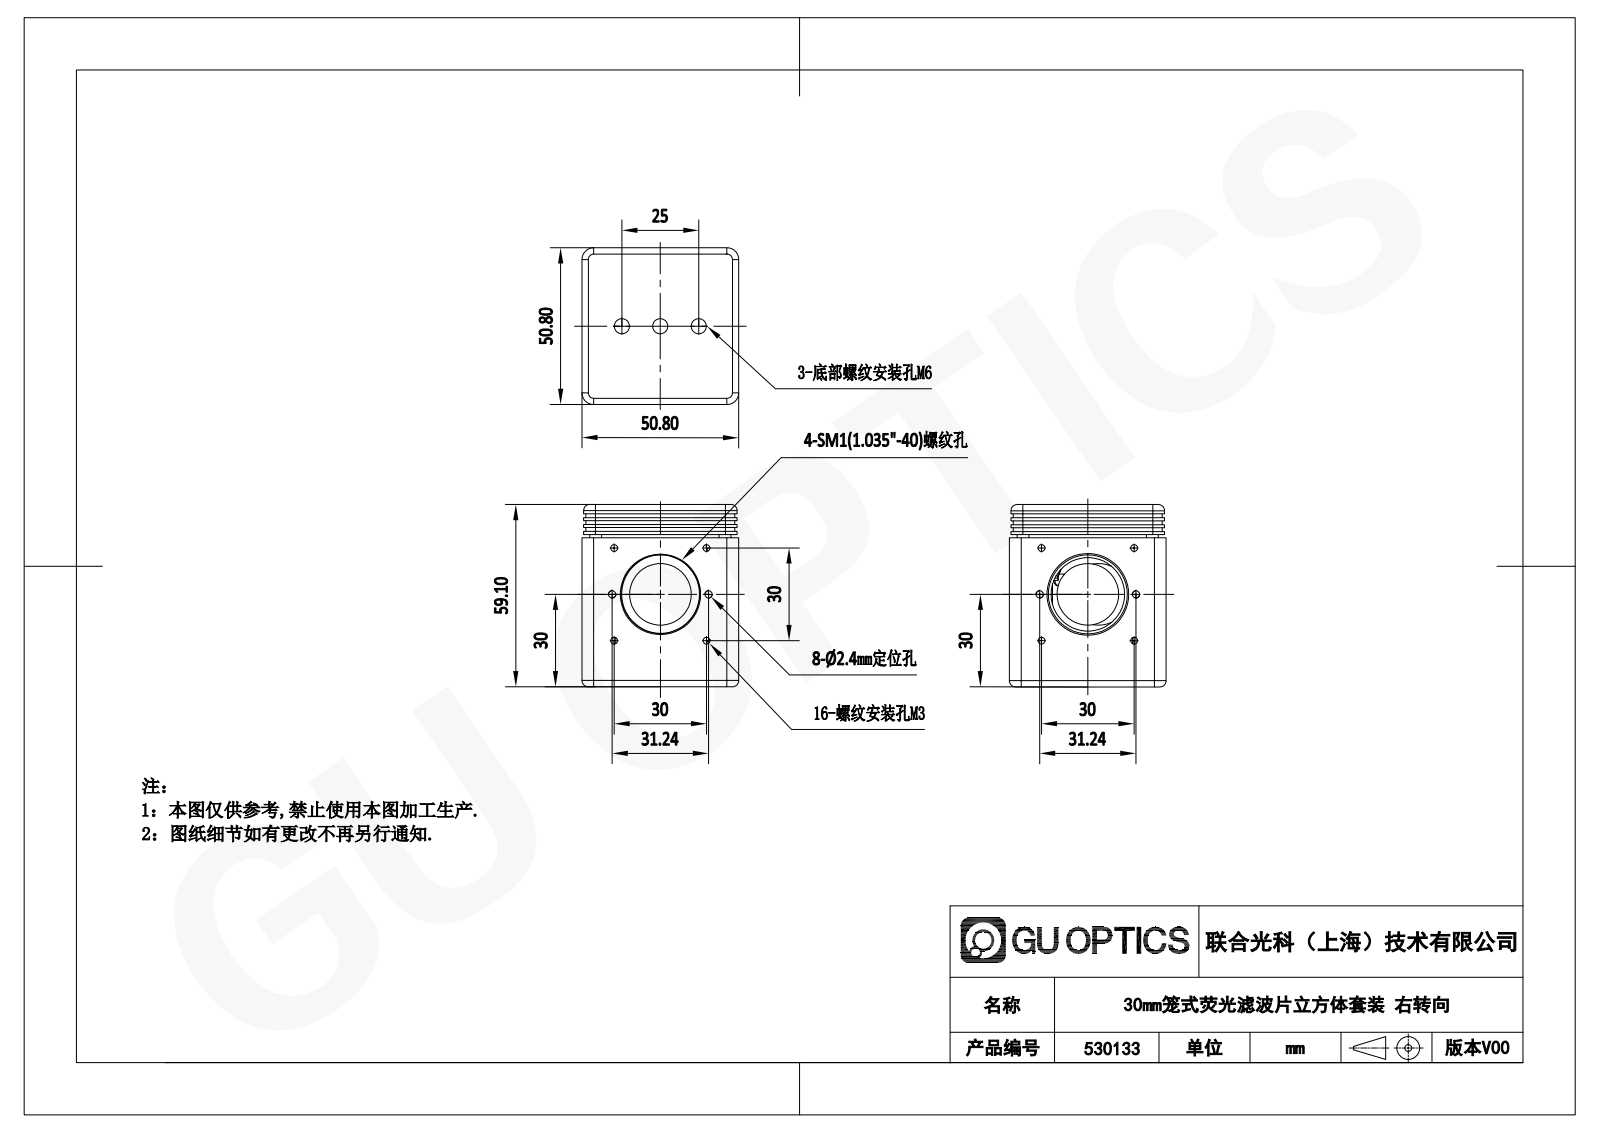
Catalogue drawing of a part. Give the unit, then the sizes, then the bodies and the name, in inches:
Units: inches
Overall size (bounding box): 2.328 × 2 × 2
Round holes (diameter × count): ⌀0.098 ×11, ⌀0.197 ×6, ⌀0.095 ×4, ⌀0.2 ×4, ⌀0.134 ×3, ⌀0.157 ×3, ⌀0.22 ×3, ⌀1.008 ×3, ⌀0.063 ×2, ⌀0.08 ×2, ⌀0.081 ×2, ⌀0.114 ×2
Round bosses / shafts (diameter × count): ⌀0.059 ×6, ⌀0.217 ×3, ⌀0.118 ×3, ⌀0.181 ×1, ⌀0.098 ×1, ⌀0.079 ×1
Partial cylindrical surfaces — rounded edges, fillets, slot ends (radius × count): R0.125 ×29, R0.135 ×17, R0.15 ×16, R0.031 ×12, R0.25 ×9, R0.063 ×8, R0.08 ×8, R0.07 ×4
Main face-to-face distances: 0.15, 1.85, 0.05, 2, 0.1, 2.328, 1.7, 0.025, 1.825, 0.175
Hole centre spacings: 0.591, 0.835, 1.181, 1.343, 1.299, 0.571, 0.615, 1.433
Volume: 5.057 in³ · Surface area: 81.98 in²
Bodies: 23 solids, 862 faces (461 planar, 260 cylindrical, 141 other)
Part name (STEP PRODUCT): 530133
STEP written by: SolidWorks 2020 (CONFIG_CONTROL_DESIGN)
